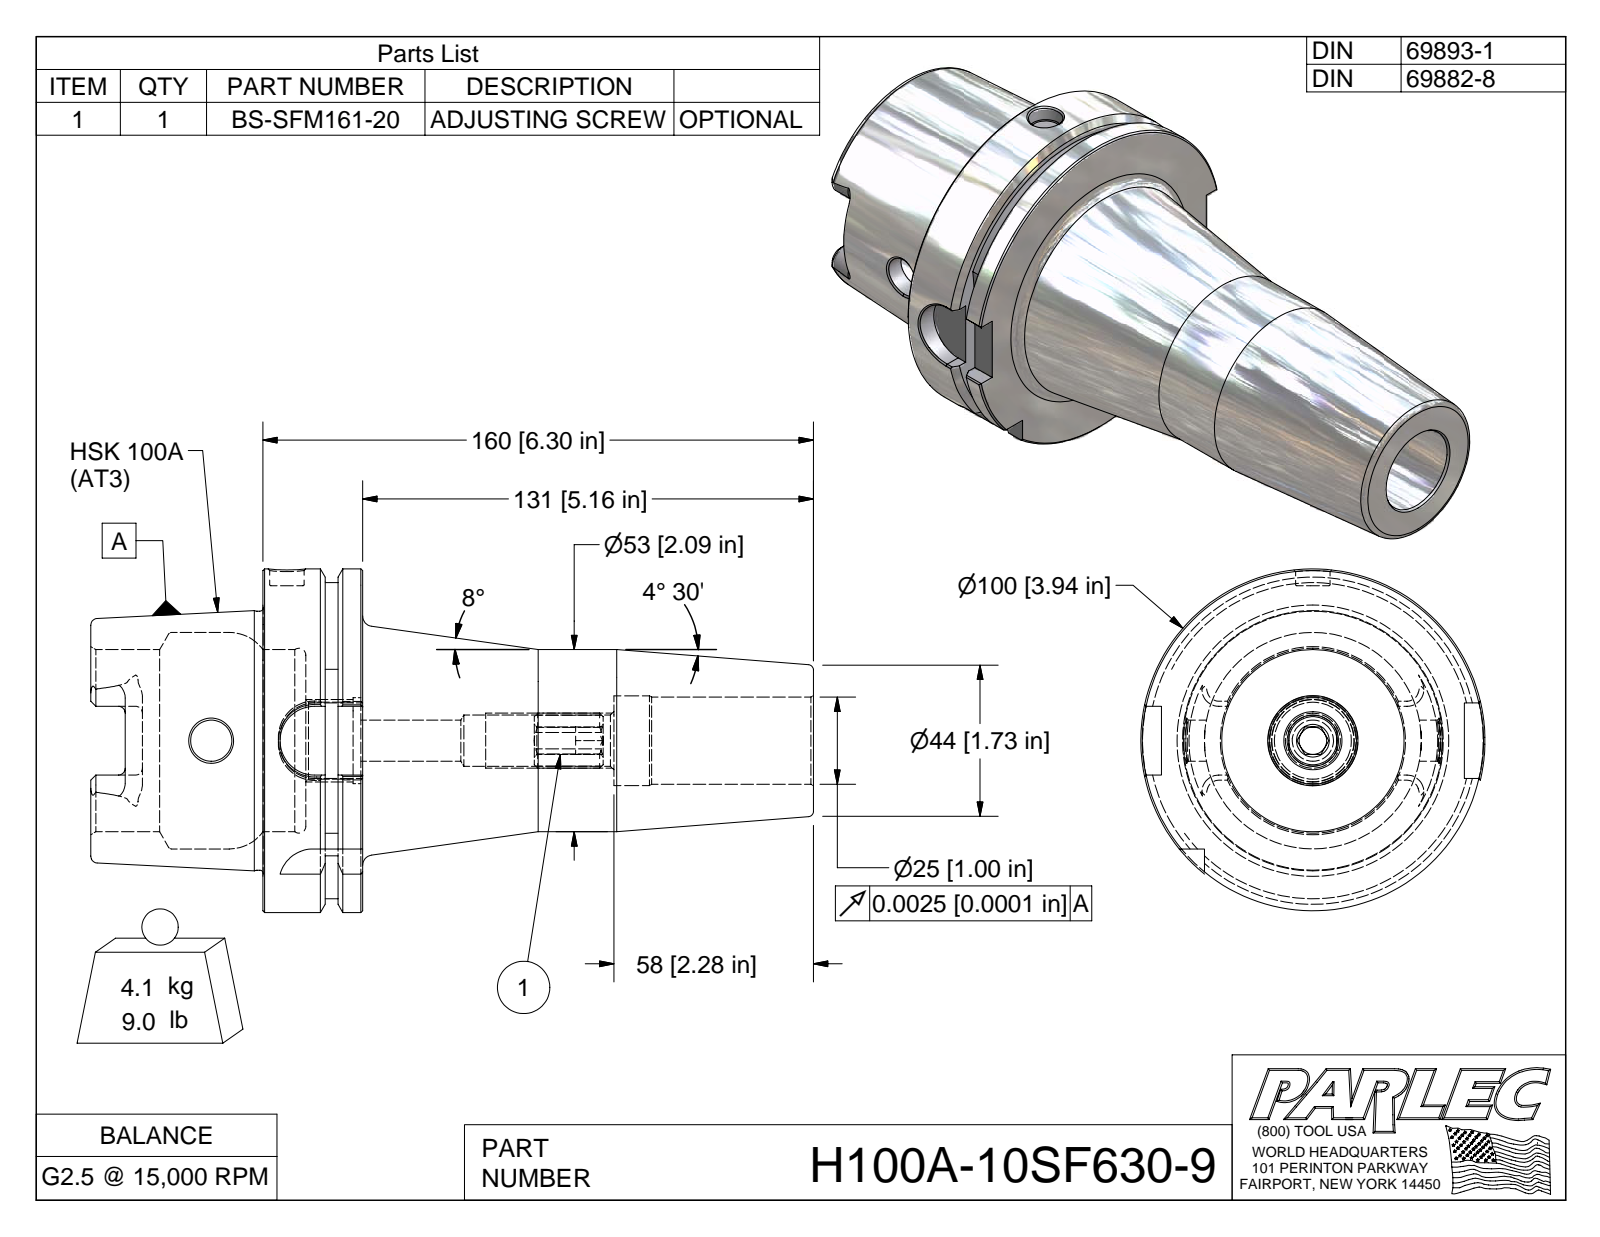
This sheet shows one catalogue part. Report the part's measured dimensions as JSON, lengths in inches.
{"part_name": "H100A-10SF630-9; H100A-10SF630-9-1; BS-SFM161-20", "step_written_by": "Autodesk Inventor 2009 (AUTOMOTIVE_DESIGN)", "units": "inches", "bodies": {"solids": 2, "faces": 150, "planar": 49, "cylindrical": 30, "other": 71}, "overall_size": [8.269, 3.937, 3.937], "volume_in3": 31.62, "surface_area_in2": 123, "round_holes": [[0.394, 1], [0.472, 1], [0.881, 1], [0.985, 1], [0.999, 1], [1.029, 1], [2.087, 1], [2.48, 1]], "round_bosses_or_shafts": [[3.937, 1], [2.967, 1]], "partial_cylinders_radius": [[0.394, 4], [0.079, 3], [0.192, 2], [0.315, 1], [1.811, 1]], "face_to_face_distances": [1.142, 0.492, 0.65, 1.969, 2.461, 3.11, 8.269, 6.3, 5.808, 5.158]}
